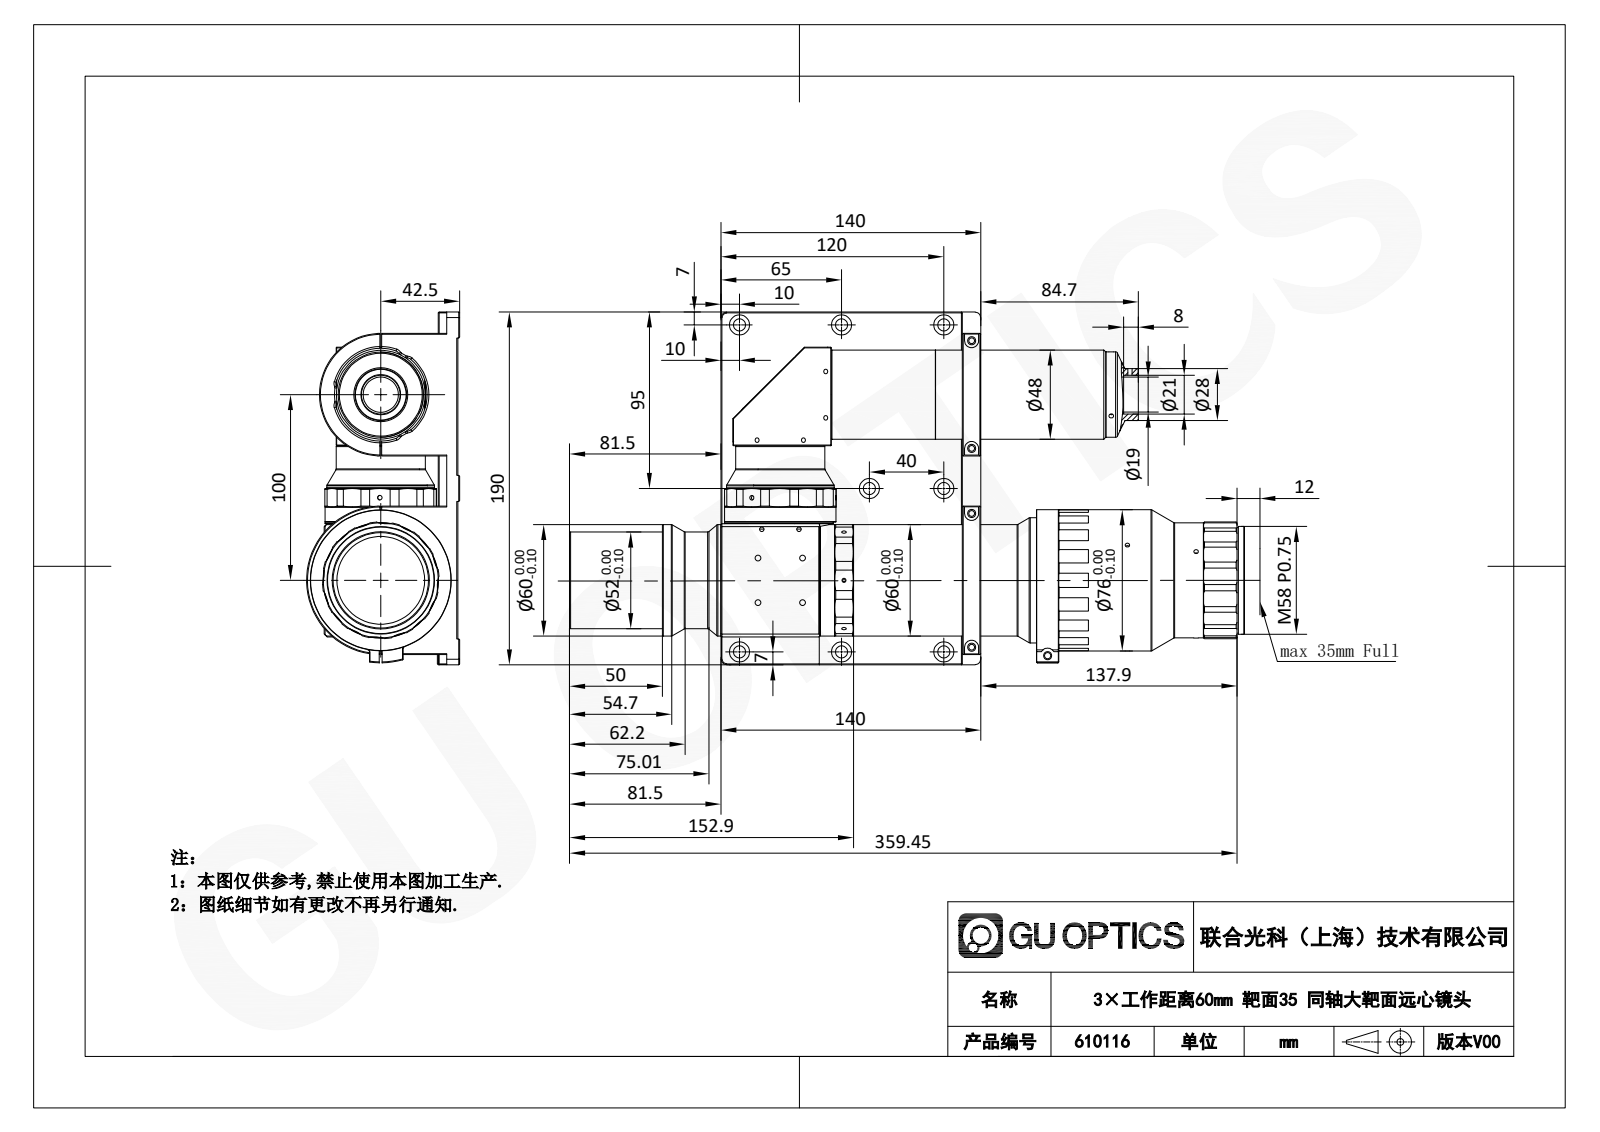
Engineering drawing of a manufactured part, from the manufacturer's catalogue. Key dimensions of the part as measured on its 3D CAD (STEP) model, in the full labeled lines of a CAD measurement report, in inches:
STEP written by: SolidWorks 2017 (CONFIG_CONTROL_DESIGN)
Units: inches
Bodies: 1 solid, 1364 faces (398 planar, 488 cylindrical, 478 other)
Overall size (bounding box): 14.309 × 7.48 × 3.249
Volume: 115.2 in³ · Surface area: 341.4 in²
Round holes (diameter × count): ⌀0.098 ×22, ⌀0.13 ×19, ⌀0.177 ×16, ⌀0.295 ×11, ⌀0.094 ×10, ⌀0.256 ×8, ⌀0.433 ×8, ⌀0.126 ×4, ⌀0.236 ×4, ⌀0.059 ×2, ⌀0.087 ×2, ⌀0.134 ×1
Round bosses / shafts (diameter × count): ⌀2.362 ×2, ⌀2.283 ×2, ⌀1.89 ×2, ⌀2.992 ×1, ⌀2.835 ×1, ⌀2.795 ×1, ⌀2.657 ×1, ⌀2.252 ×1
Partial cylindrical surfaces — rounded edges, fillets, slot ends (radius × count): R0.591 ×34, R0.079 ×16, R0.118 ×10, R0.197 ×6, R0.148 ×4, R0.039 ×2, R0.827 ×2, R1.201 ×2
Main face-to-face distances: 0.413, 0.453, 0.039, 2.835, 0.394, 2.421, 0.256, 2.874, 5.512, 5.118
Hole centre spacings: 0.945, 1.575, 0.197, 0.236, 1.336, 1.63, 1.642, 1.772
